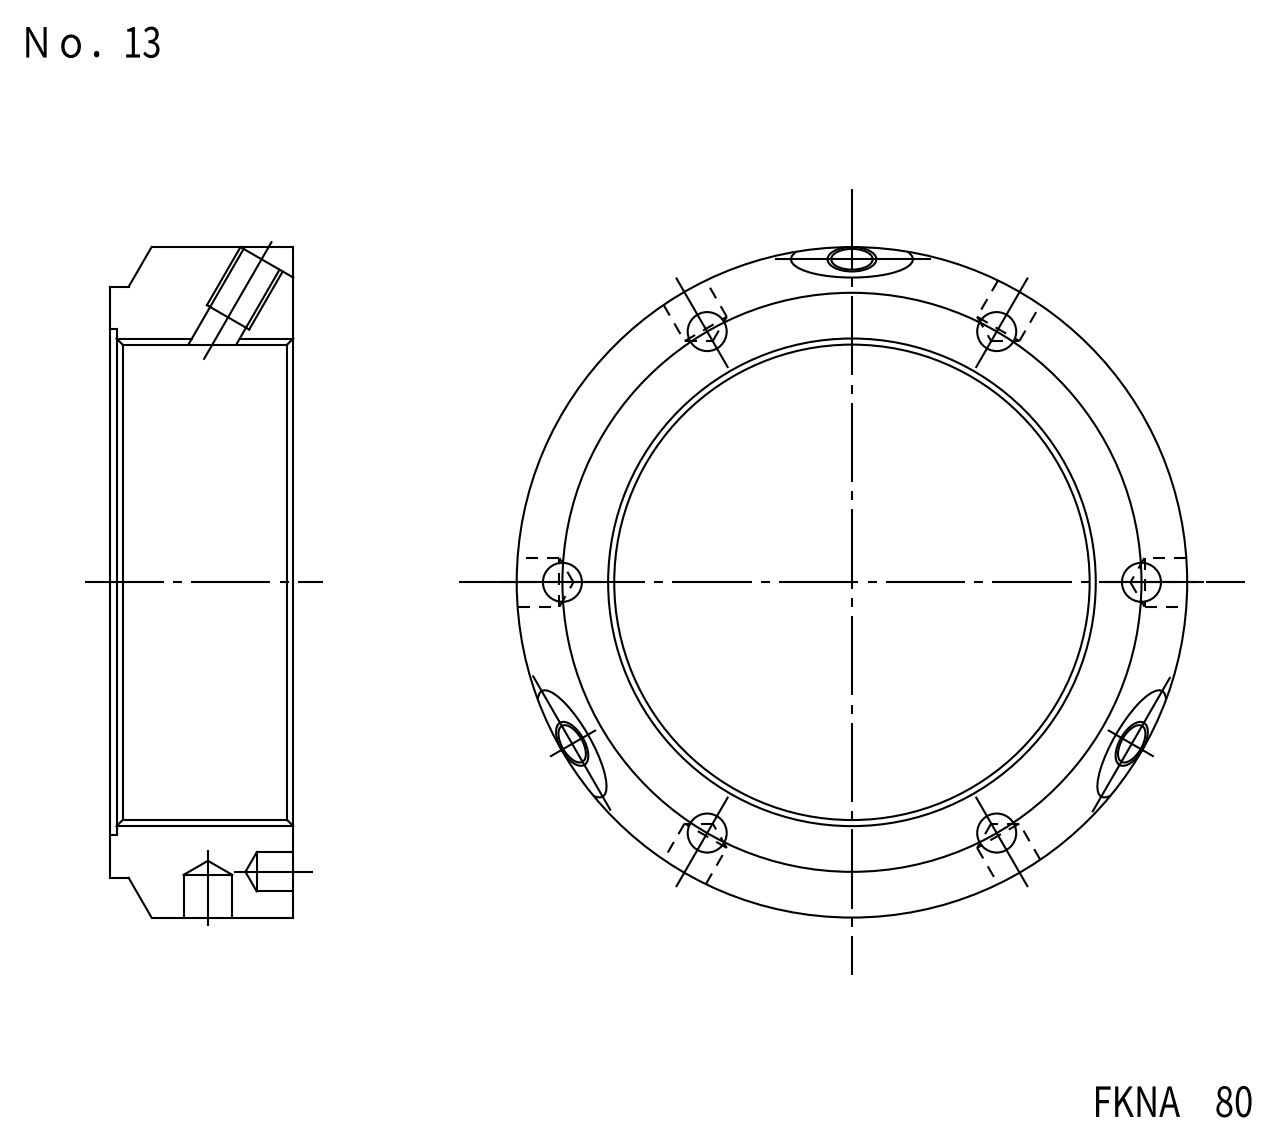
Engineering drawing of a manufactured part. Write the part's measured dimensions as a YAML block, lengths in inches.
part_name: "FKD FKNA80"
step_written_by: "Autodesk Inventor LT (CONFIG_CONTROL_DESIGN)"
units: inches
bodies: {solids: 1, faces: 44, planar: 6, cylindrical: 25, other: 13}
overall_size: [4.331, 4.331, 1.181]
volume: 7.442
surface_area: 43.55
round_holes:
  - {diameter: 0.252, count: 6}
  - {diameter: 0.262, count: 3}
  - {diameter: 0.315, count: 3}
  - {diameter: 0.323, count: 3}
  - {diameter: 3.15, count: 1}
  - {diameter: 3.268, count: 1}
round_bosses_or_shafts:
  - {diameter: 4.331, count: 1}
  - {diameter: 3.819, count: 1}
partial_cylinders:
  - {radius: 0.787, count: 3}
face_to_face_distances: [1.181, 0.059, 1.122]
hole_center_spacings: [1.87, 3.239, 3.239, 3.741, 3.74]
